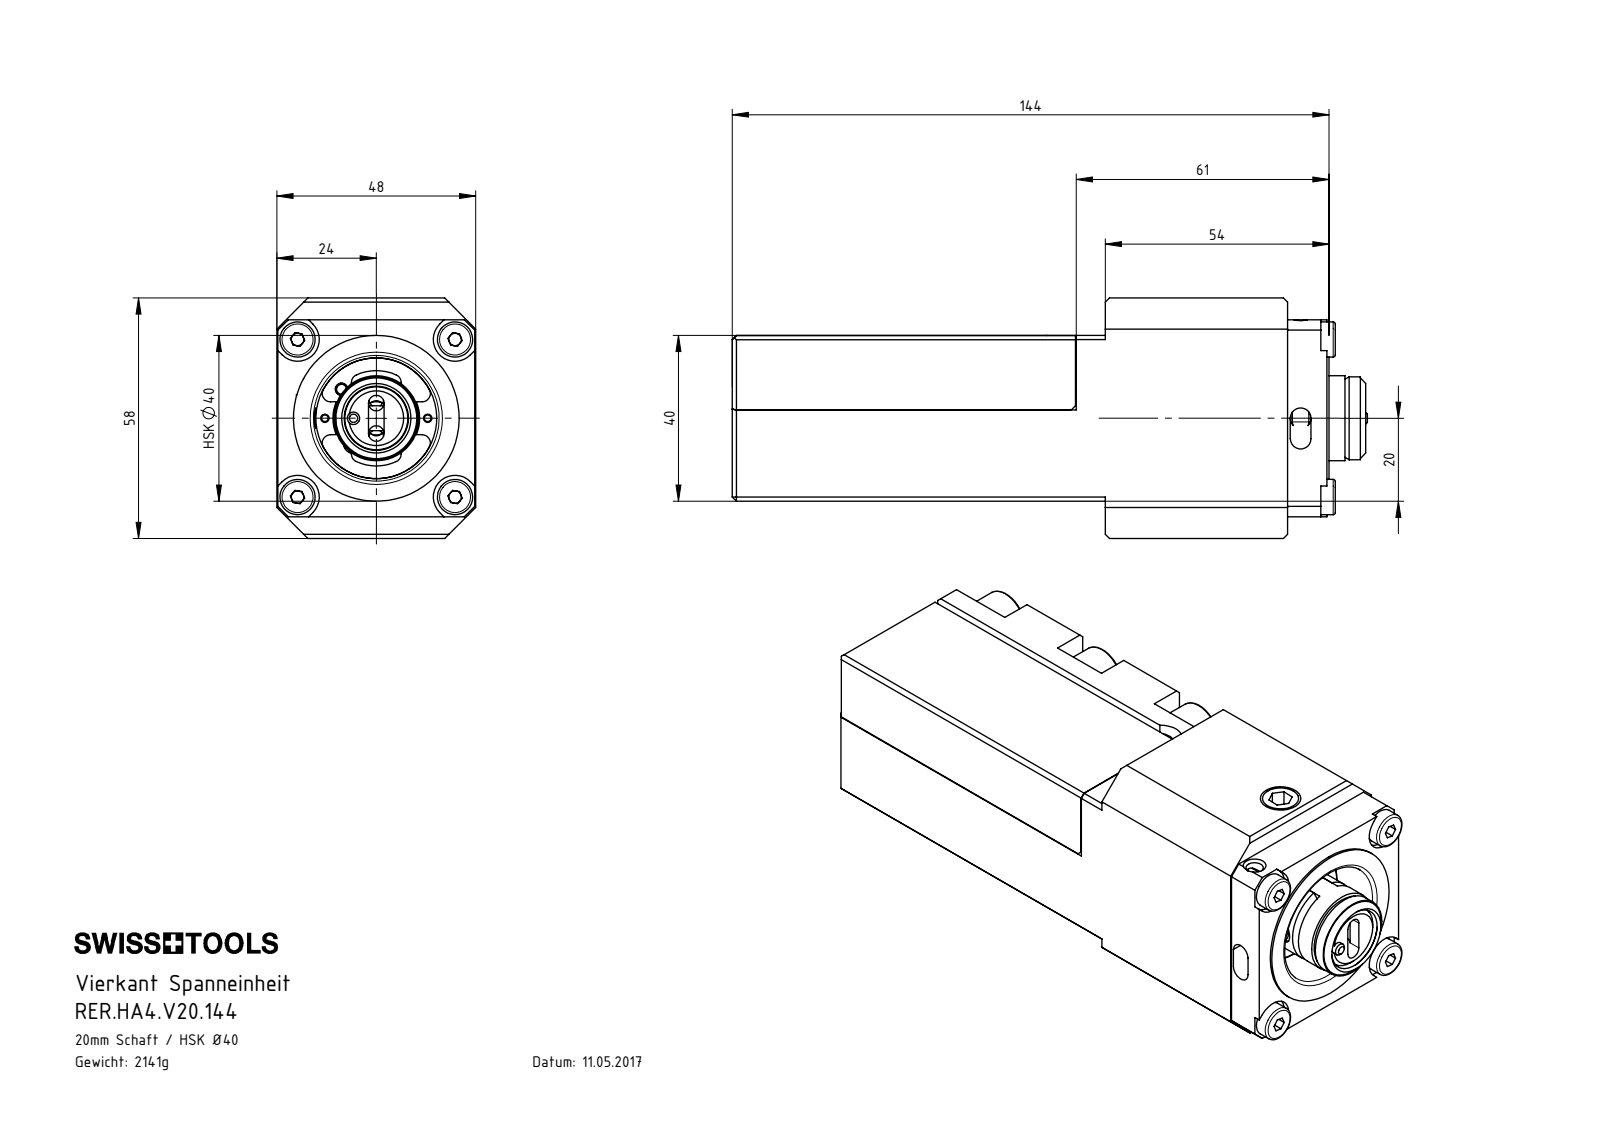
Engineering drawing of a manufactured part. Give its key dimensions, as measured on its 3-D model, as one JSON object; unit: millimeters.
{"part_name": "ISO 4762 - M8 x 35; RER-HA4.V20.140-11_A; DIN 3771 - 36x2; DIN 916 - G1-8 x 8 (+8 more)", "step_written_by": "SolidWorks 2022 (AUTOMOTIVE_DESIGN)", "units": "millimeters", "bodies": {"solids": 24, "faces": 715, "planar": 300, "cylindrical": 205, "other": 210}, "overall_size": [153.26, 58, 48], "volume_mm3": 292636, "surface_area_mm2": 81900, "round_holes": [[4.2, 5], [5.5, 4], [6.8, 3], [9, 3], [1.6, 2], [3, 2], [3.3, 2], [3.5, 2], [3.75, 2], [2.4, 1], [4, 1], [5, 1]], "round_bosses_or_shafts": [[5, 5], [8.5, 4], [13, 3], [8, 3], [40, 1], [39.6, 1], [39.5, 1], [37.8, 1]], "partial_cylinders_radius": [[1, 8], [1.95, 4], [2, 4], [5.25, 4], [7.5, 3], [2.75, 2], [0.5, 1], [1.5, 1]], "face_to_face_distances": [48, 9, 39.93, 49, 42, 92, 134, 47.89, 48.93, 58], "hole_center_spacings": [33, 12.93, 20.11, 24.41, 26.87, 29.59, 36.7, 38]}
